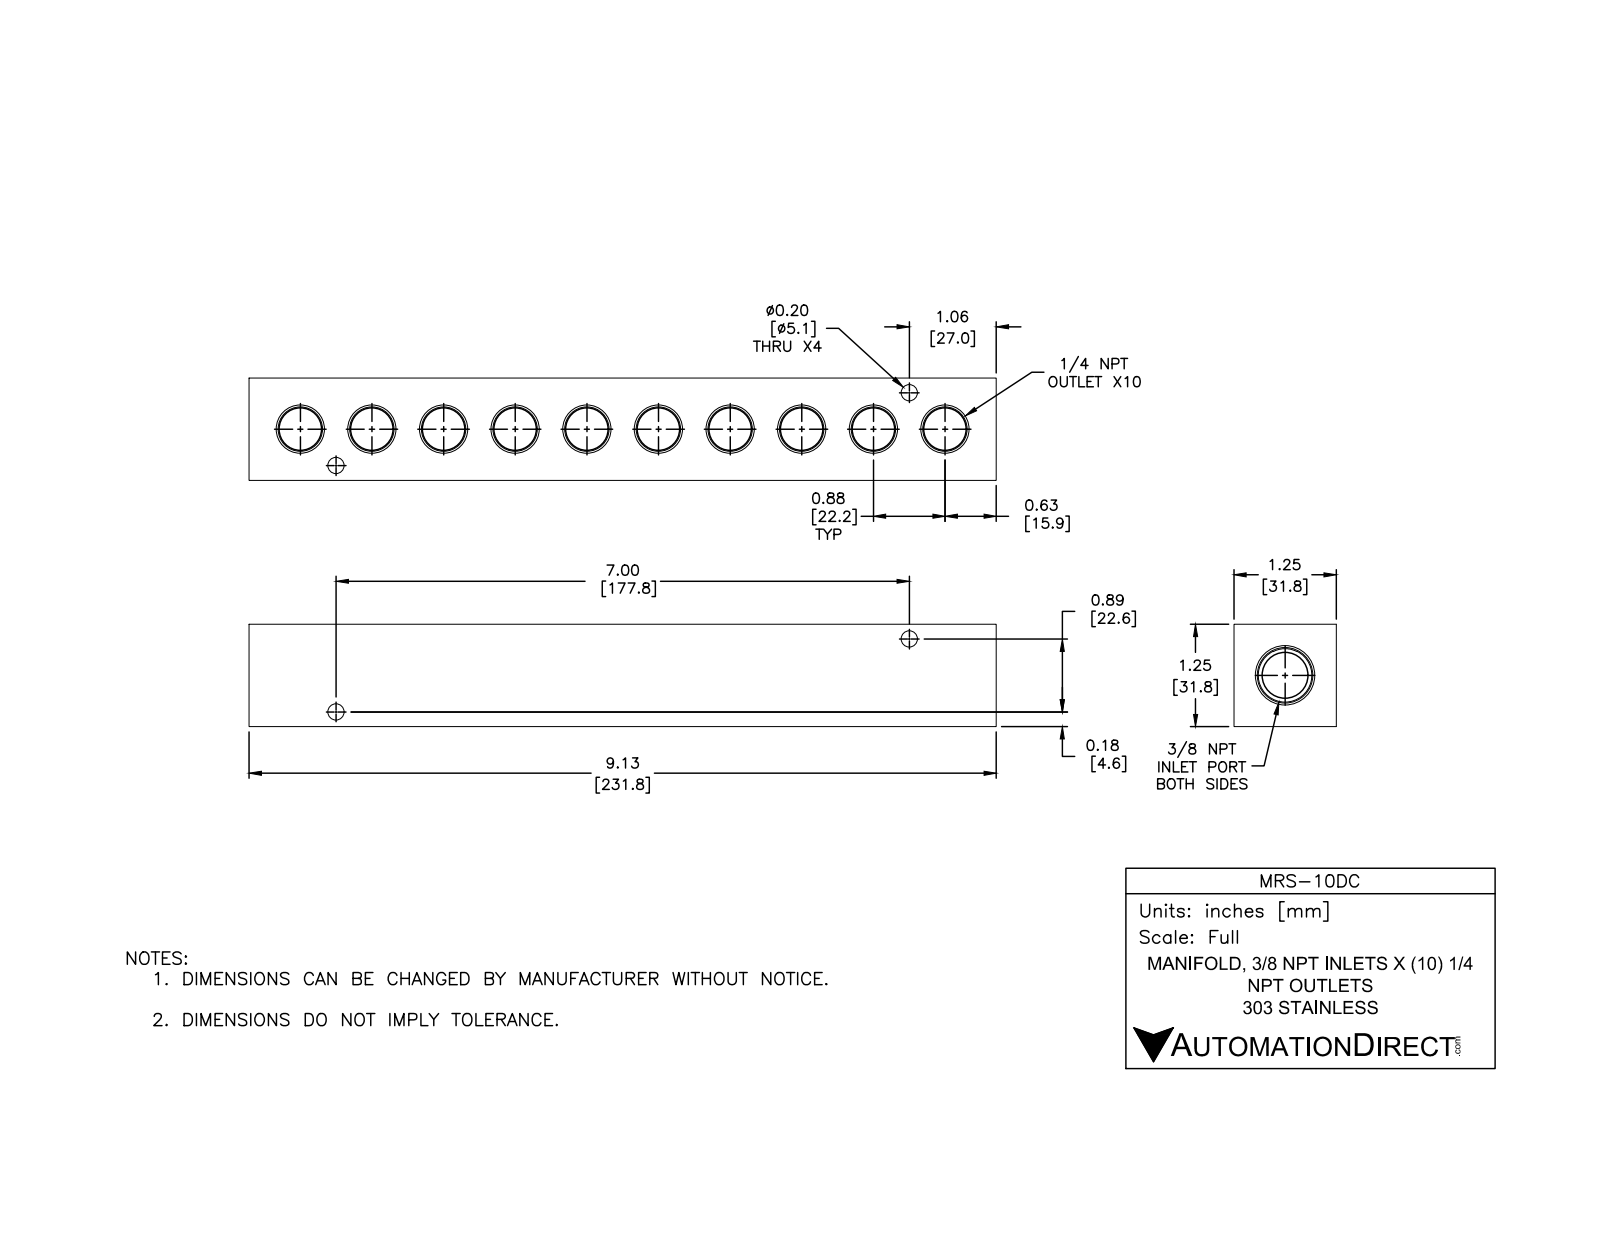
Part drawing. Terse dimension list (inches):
name: MRS-10DC
written by: SolidWorks 2015 (CONFIG_CONTROL_DESIGN)
unit: in
bodies: 1 solid, 114 faces (28 planar, 38 cylindrical, 48 other)
size: 9.125 × 1.25 × 1.25
volume: 10.94 in³; area: 69.43 in²
holes: 4× ⌀0.2, 1× ⌀0.562
rounds: 10× R0.219
face distances: 1.25, 9.125, 0.86, 0.39, 0.41, 8.715, 8.305
hole spacings: 7.056
